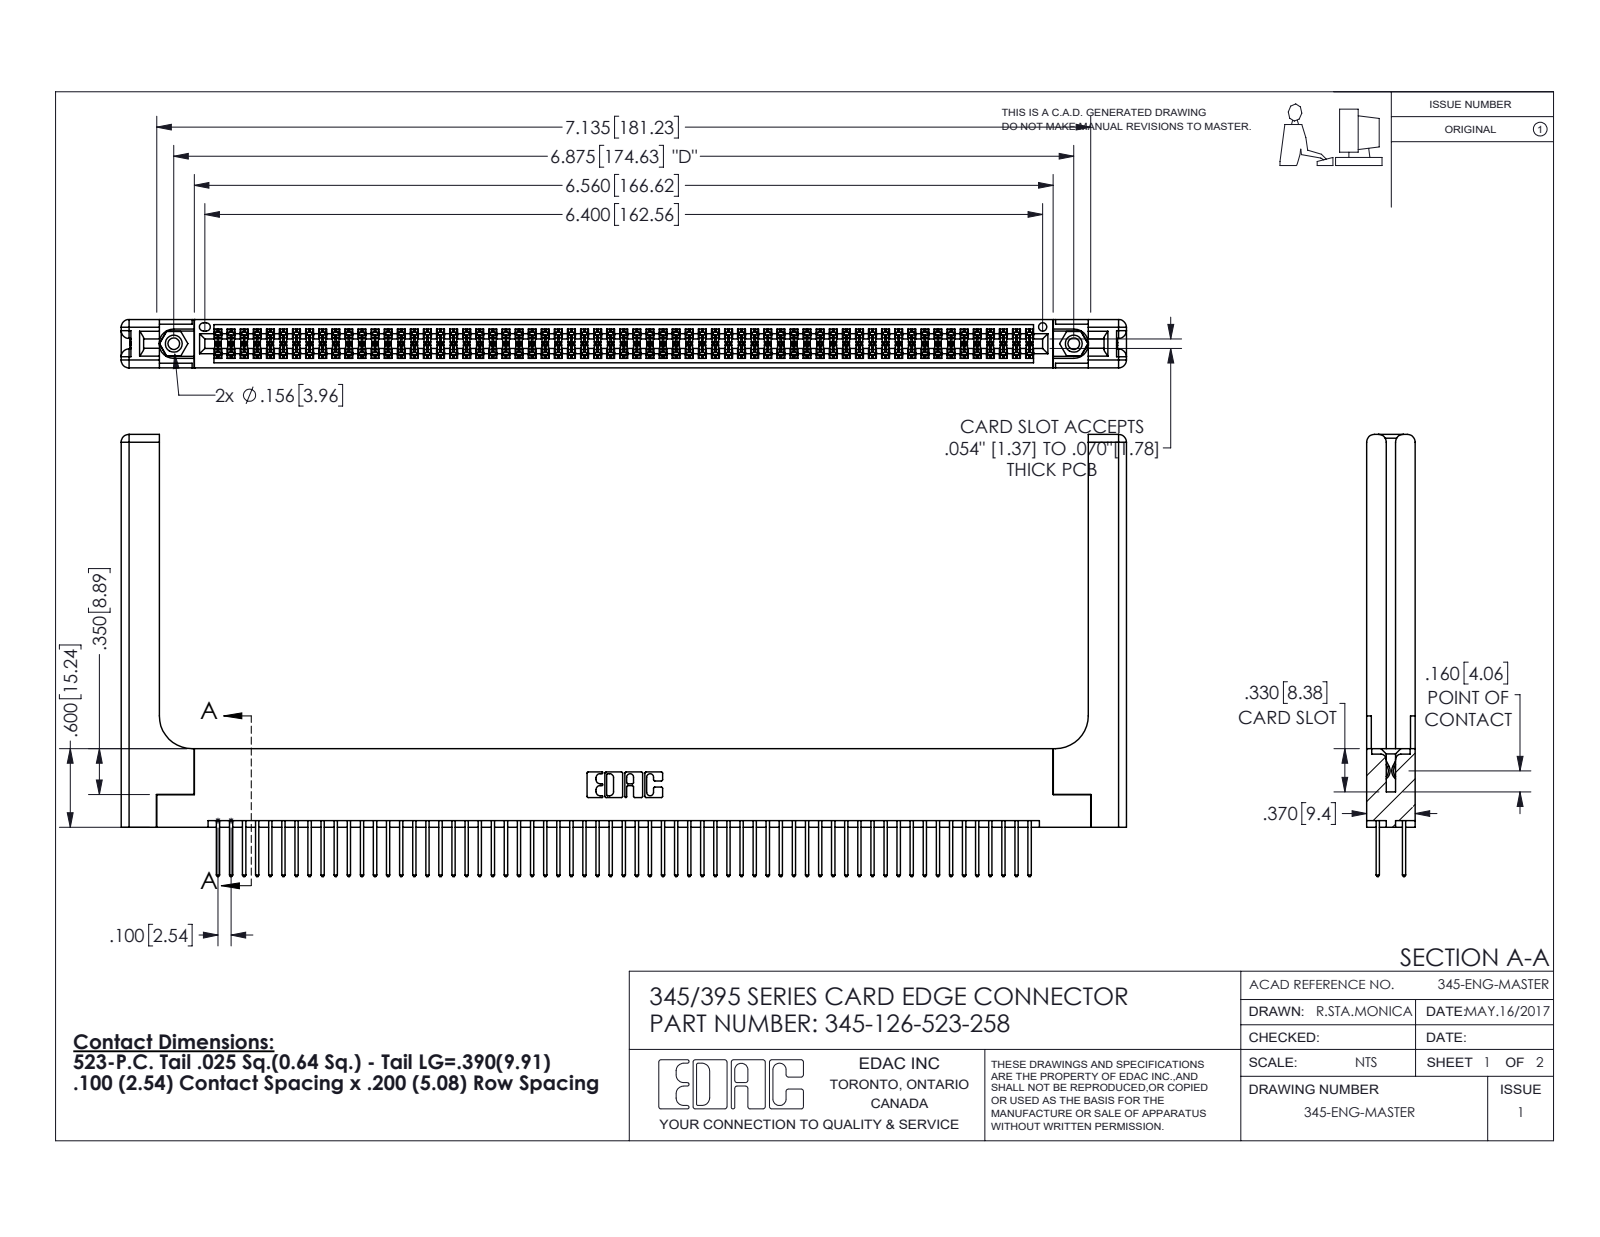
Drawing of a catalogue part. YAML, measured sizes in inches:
part_name: "345-220-058_345-220-058; 345 Part_Flush Mounting Lugs - 0.156 Dia-TH; 345-292-001_345-293-123; 345-126-523-258 (+1 more)"
step_written_by: "SolidWorks 2016 (CONFIG_CONTROL_DESIGN)"
units: inches
bodies: {solids: 131, faces: 6682, planar: 4386, cylindrical: 2236, other: 60}
overall_size: [7.679, 3.377, 0.37]
volume: 1.701
surface_area: 54.72
round_holes:
  - {diameter: 0.089, count: 2}
  - {diameter: 0.125, count: 2}
  - {diameter: 0.156, count: 2}
  - {diameter: 0.064, count: 1}
round_bosses_or_shafts:
  - {diameter: 0.155, count: 2}
partial_cylinders:
  - {radius: 0.006, count: 189}
  - {radius: 0.01, count: 126}
  - {radius: 0.01, count: 22}
  - {radius: 0.06, count: 16}
  - {radius: 0.007, count: 6}
  - {radius: 0.031, count: 6}
  - {radius: 0.026, count: 3}
  - {radius: 0.014, count: 2}
face_to_face_distances: [0.072, 0.298, 0.37, 0.2, 0.098, 0.272, 0.025, 0.225, 0.175, 0.148]
hole_center_spacings: [0.27, 6.639, 6.875]
